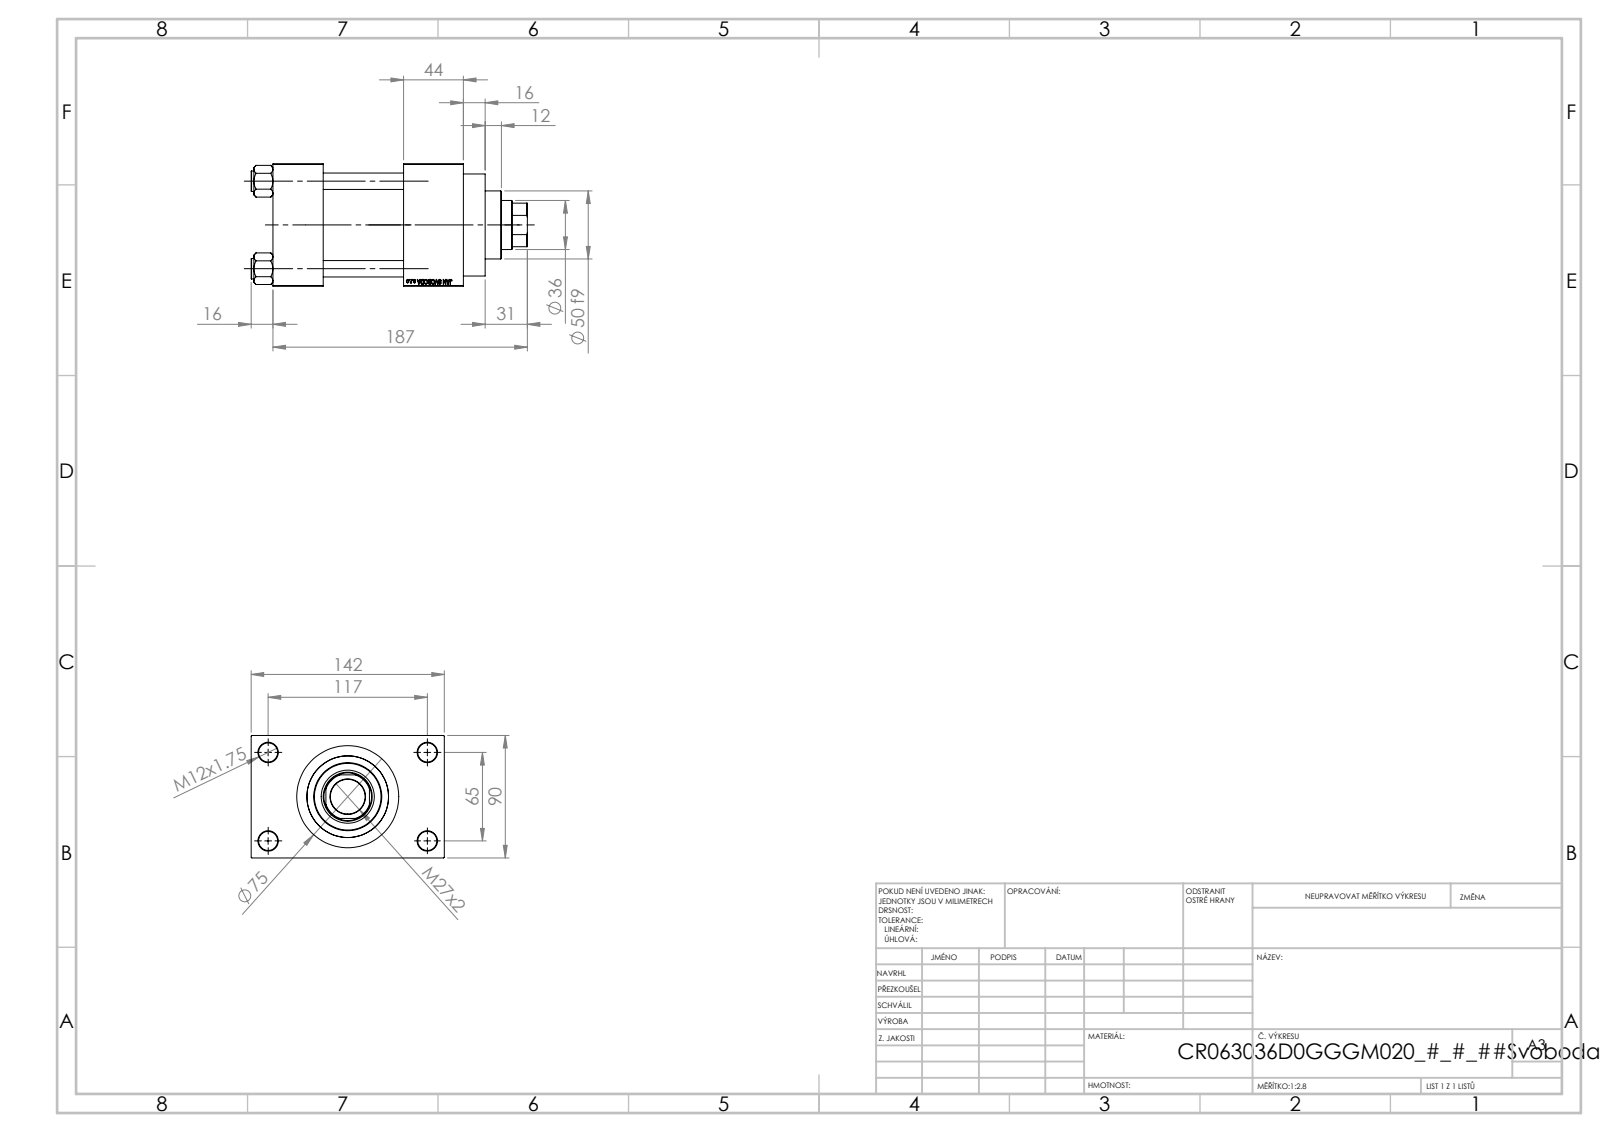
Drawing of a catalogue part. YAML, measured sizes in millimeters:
part_name: "NUT_M5_D; V215CR_D_Body; V215CR_D_TYCINKA; V215_VC_A (+1 more)"
step_written_by: "SolidWorks 2019 (CONFIG_CONTROL_DESIGN)"
units: millimeters
bodies: {solids: 11, faces: 1104, planar: 497, cylindrical: 89, other: 518}
overall_size: [203, 142, 90]
volume: 1120000
surface_area: 204077
round_holes:
  - {diameter: 12, count: 4}
  - {diameter: 14, count: 4}
  - {diameter: 7, count: 2}
  - {diameter: 20.96, count: 2}
  - {diameter: 30, count: 2}
  - {diameter: 25.5, count: 1}
  - {diameter: 36, count: 1}
  - {diameter: 39, count: 1}
  - {diameter: 50, count: 1}
  - {diameter: 60, count: 1}
  - {diameter: 63, count: 1}
round_bosses_or_shafts:
  - {diameter: 15, count: 4}
  - {diameter: 75, count: 1}
  - {diameter: 69, count: 1}
partial_cylinders:
  - {radius: 17.5, count: 1}
face_to_face_distances: [90, 59, 37, 96, 140, 103, 44, 26, 116, 142]
hole_center_spacings: [26.35, 45.47, 64.3, 66.92, 69.81, 90.65, 111.34, 65]
